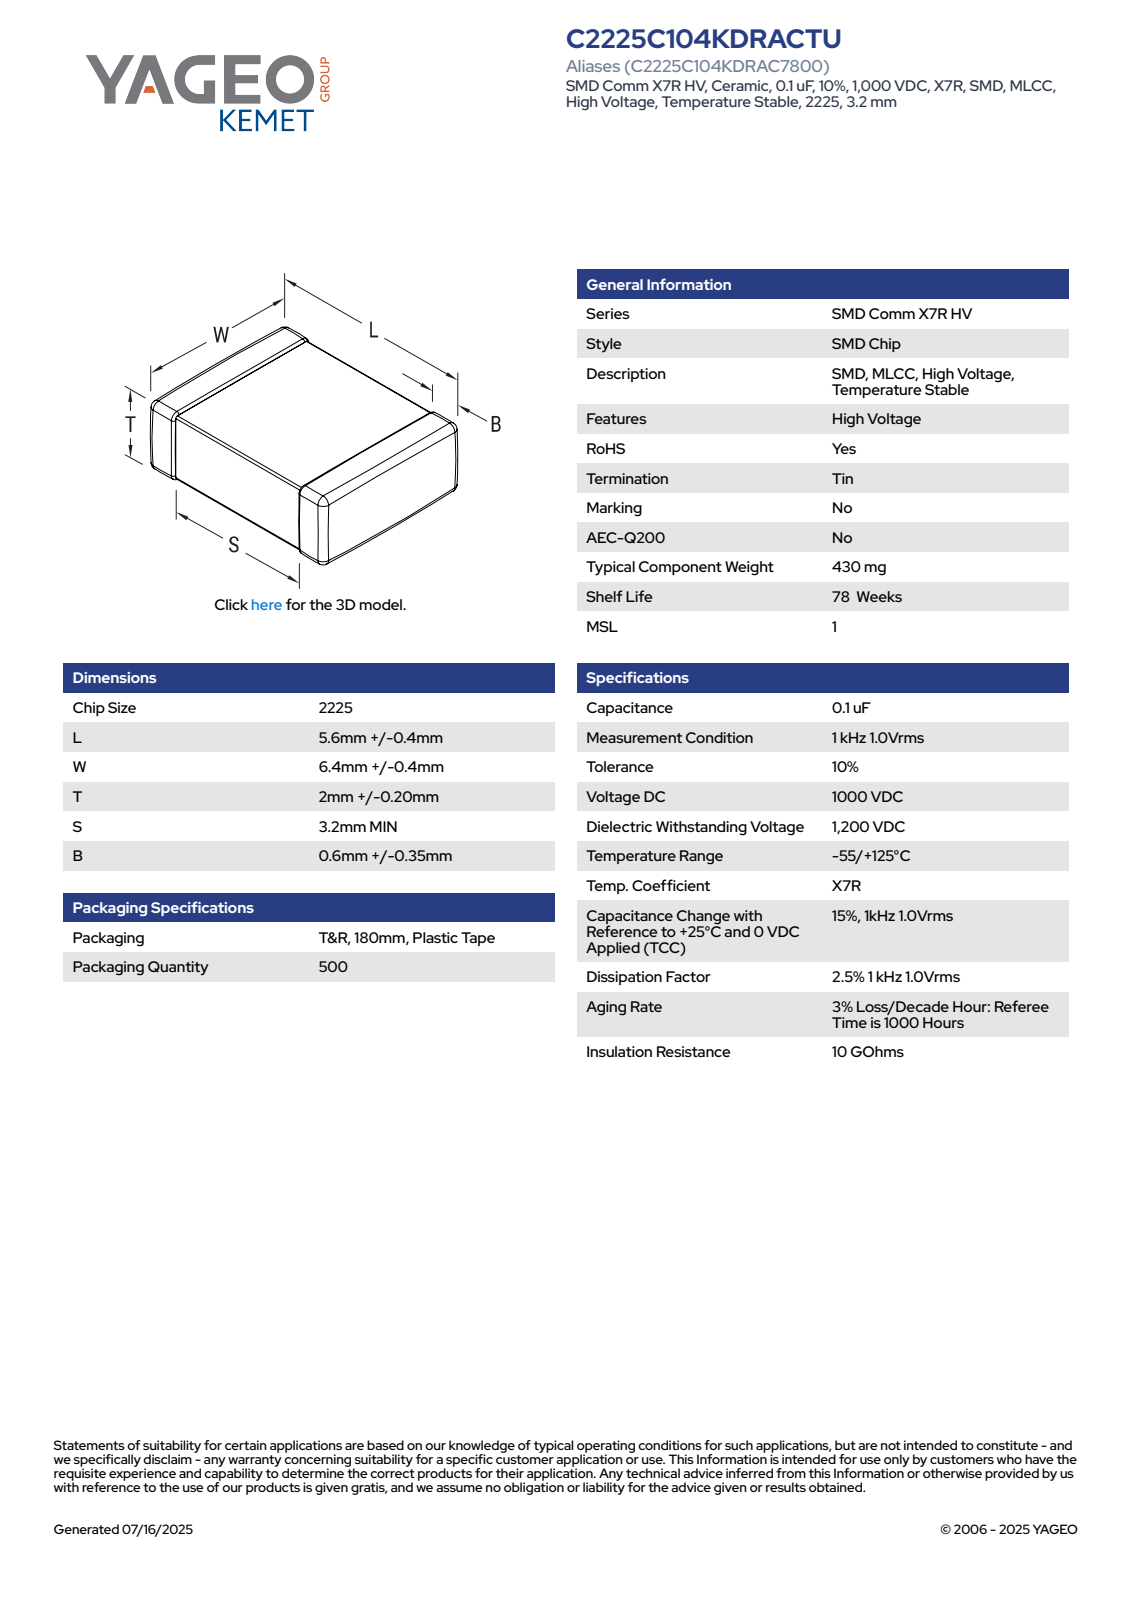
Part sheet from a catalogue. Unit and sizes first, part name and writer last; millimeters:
Units: millimetres
Overall size (bounding box): 6.8 × 6 × 2.2
Partial cylindrical surfaces — rounded edges, fillets, slot ends (radius × count): R0.14 ×24
Main face-to-face distances: 1.92, 2.06, 6, 2.2, 6.52, 6.66, 6.8, 1, 2.24, 3.76
Volume: 79 mm³ · Surface area: 138 mm²
Bodies: 4 solids, 125 faces (71 planar, 38 cylindrical, 16 other)
Part name (STEP PRODUCT): CCS_CCSTD_2225_L6W6.8T2.2B0.6
STEP written by: SolidWorks 2021 (AUTOMOTIVE_DESIGN)
